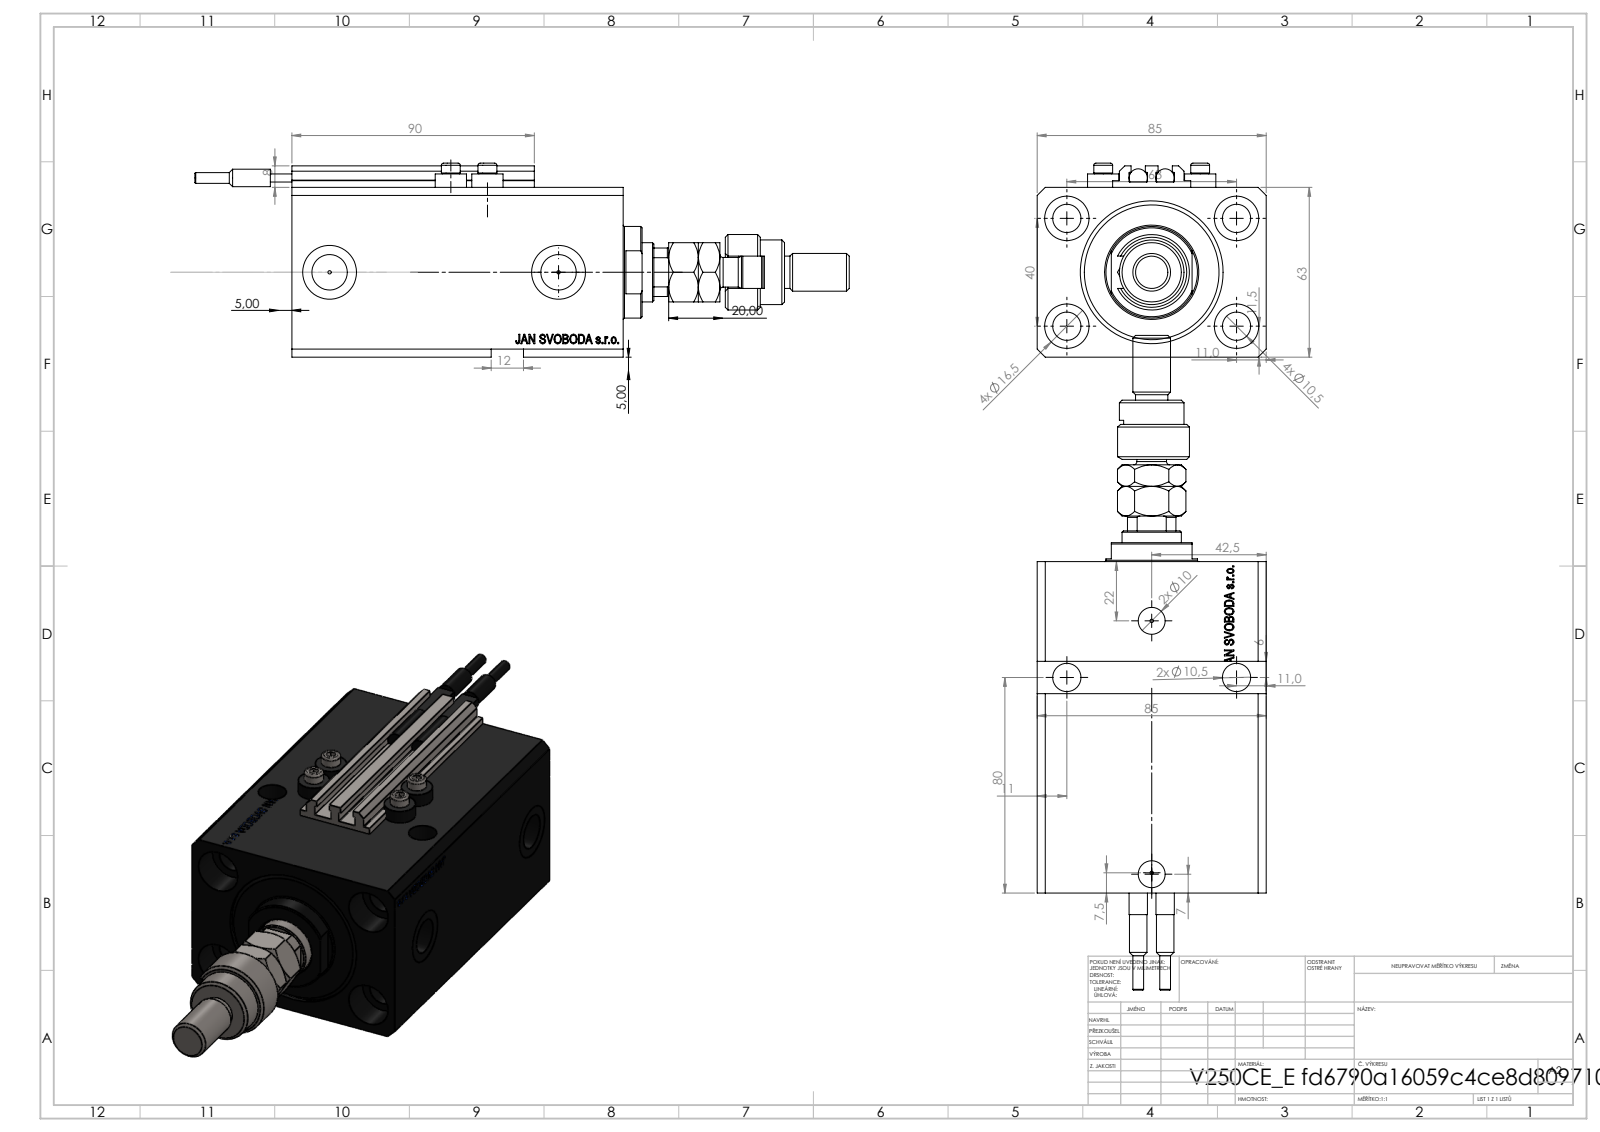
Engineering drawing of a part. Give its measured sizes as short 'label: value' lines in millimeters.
name: MFA; V250CE_VC_E; V250CE_C_VCP; V250CE_E_Body (+3 more)
written by: SolidWorks 2019 (CONFIG_CONTROL_DESIGN)
unit: mm
bodies: 12 solids, 1260 faces (599 planar, 183 cylindrical, 478 other)
size: 243 × 85 × 72
volume: 578 504 mm³; area: 131 195 mm²
holes: 8× ⌀10.5, 4× ⌀1.25, 4× ⌀4, 4× ⌀16.5, 2× ⌀10, 2× ⌀13.16, 2× ⌀20, 1× ⌀12.5, 1× ⌀22, 1× ⌀40, 1× ⌀53
bosses: 4× ⌀11.6, 4× ⌀7, 2× ⌀6.8, 2× ⌀6.5, 2× ⌀4, 1× ⌀34, 1× ⌀28, 1× ⌀24
rounds: 10× R0.2, 1× R9.75, 1× R10.5
face distances: 63, 85, 17, 123, 106, 3, 11.4, 94.6, 111.6, 65
hole spacings: 37.31, 63, 13.6, 15.4, 24.96, 27.54, 33.62, 36
